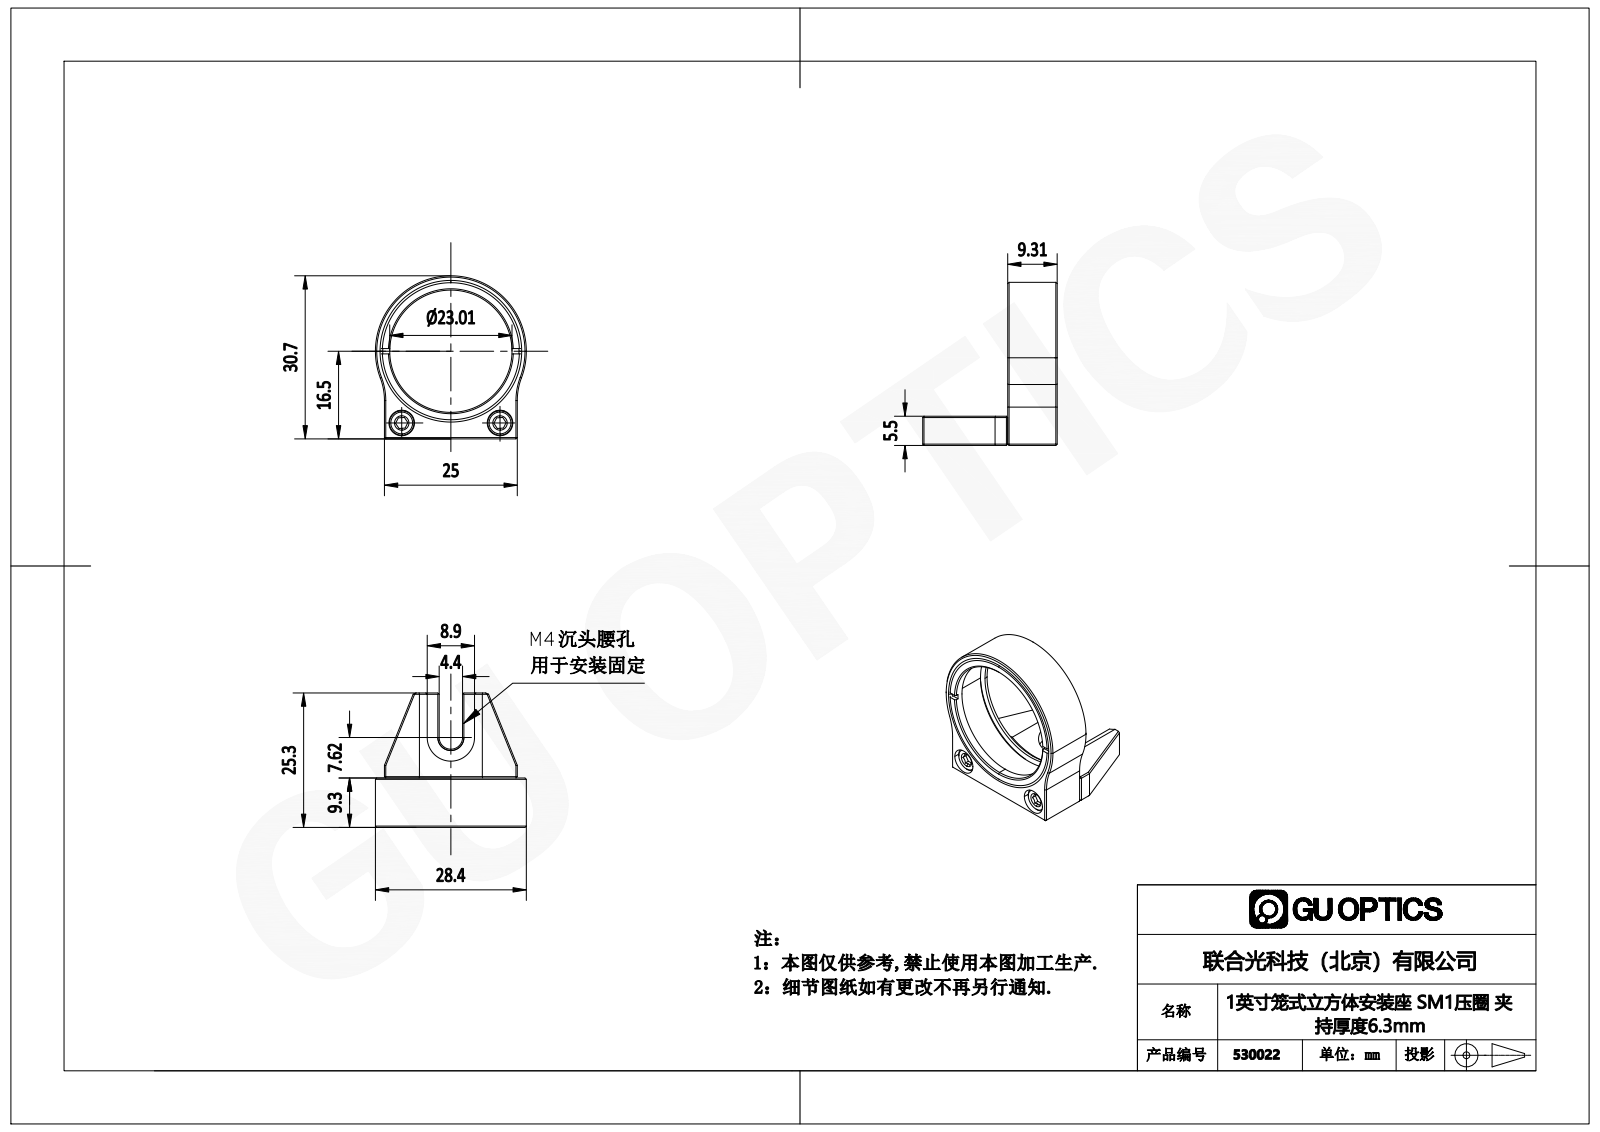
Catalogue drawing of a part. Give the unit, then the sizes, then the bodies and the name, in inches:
Units: inches
Overall size (bounding box): 1.209 × 1.118 × 0.996
Round holes (diameter × count): ⌀0.189 ×2, ⌀0.906 ×1, ⌀0.955 ×1, ⌀1.01 ×1, ⌀1.049 ×1
Partial cylindrical surfaces — rounded edges, fillets, slot ends (radius × count): R0.472 ×2, R0.087 ×1, R0.175 ×1, R0.492 ×1, R0.559 ×1
Main face-to-face distances: 0.366, 0.217, 0.287, 0.031, 0.335, 0.079, 0.256, 0.984, 0.051, 0.085
Hole centre spacings: 0.644, 0.728
Bodies: 0 solids, 155 faces (97 planar, 22 cylindrical, 36 other)
Part name (STEP PRODUCT): 2.2.7.11_L30F-Z1S6.3_1英寸光学元件安装座，带SM1螺纹孔，安装厚度6.3
STEP written by: SolidWorks 2018 (AUTOMOTIVE_DESIGN)
